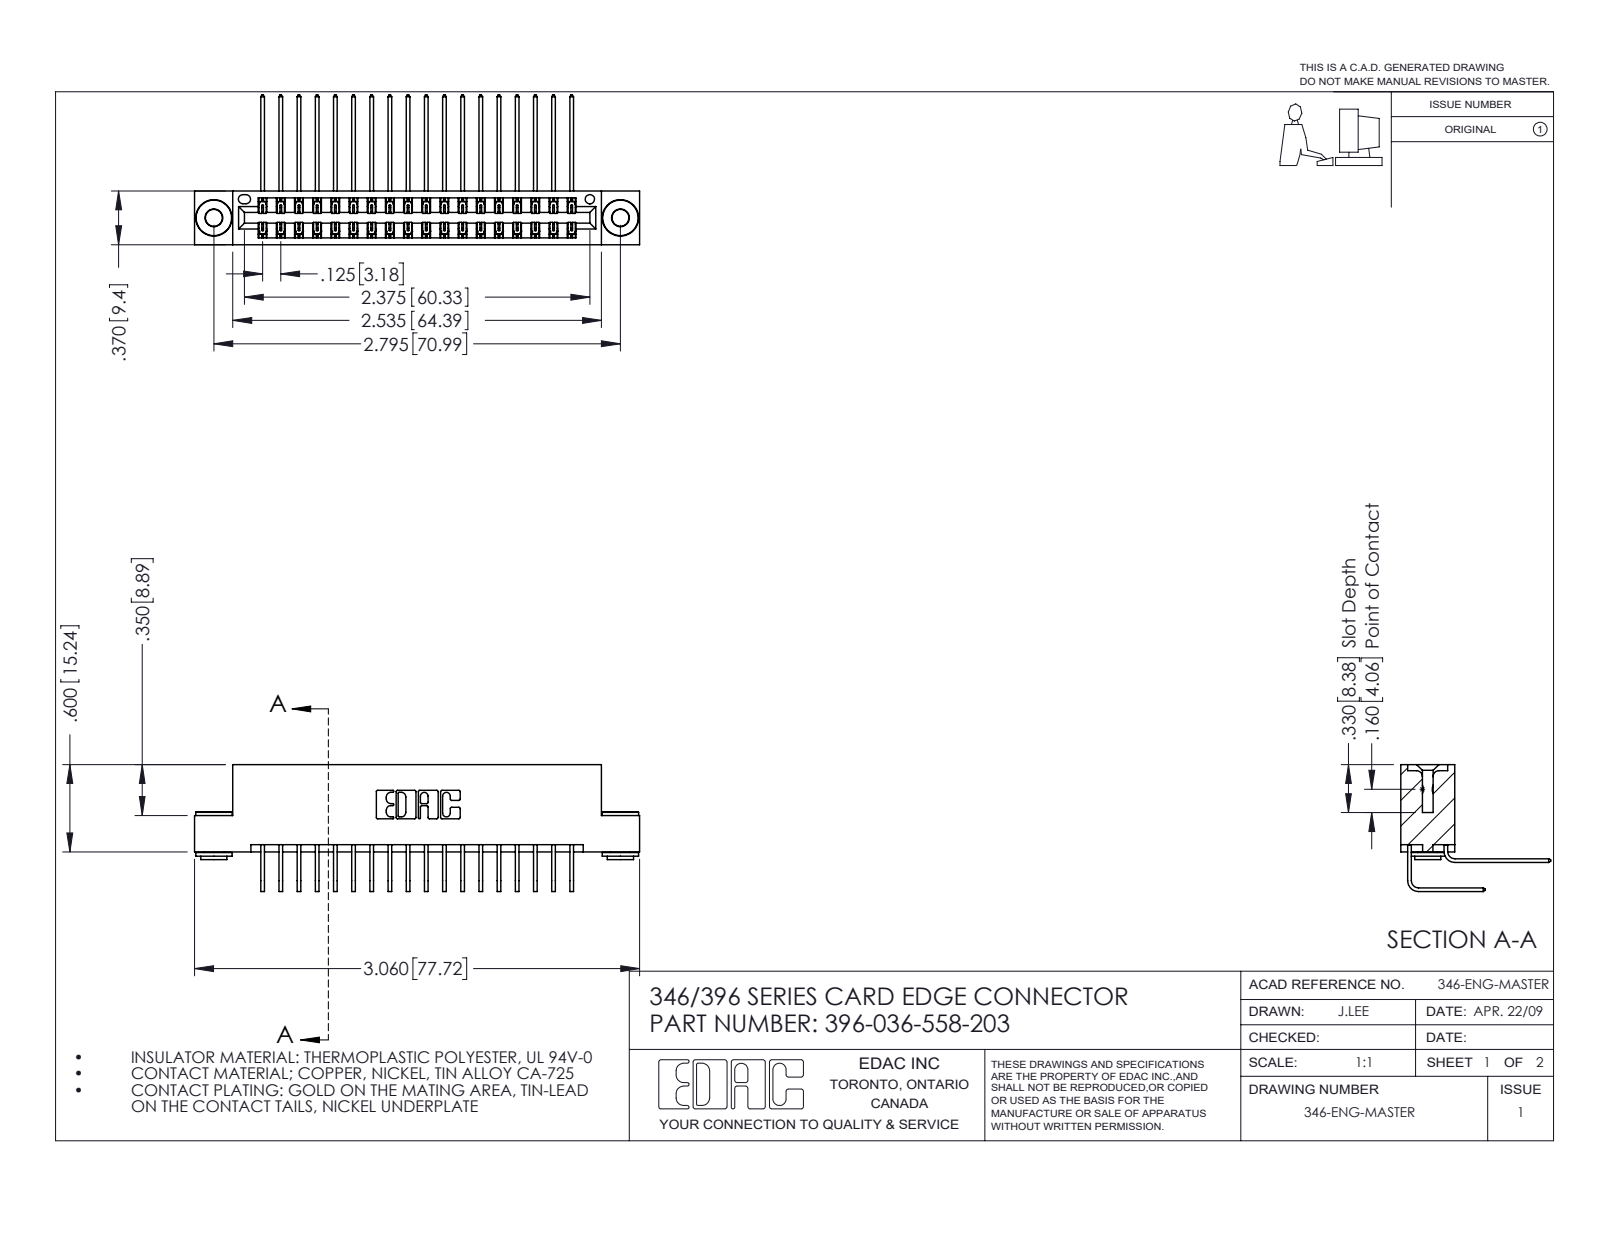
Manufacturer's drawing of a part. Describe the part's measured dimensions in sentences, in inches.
The part is named "345-250-002_345-250-002-102; 396-036-558-203; 346 Part_Flush Mounting Lugs - 0.156 Dia-TH; 345-292-001_558 Tail - 2 (+1 more)". Its 3-D file was written by "SolidWorks 2016 (CONFIG_CONTROL_DESIGN)". It is 39 solids with 2104 faces: 1418 planar, 678 cylindrical and 8 other. Overall it measures 3.06 by 1.03 by 0.873 inches. Its volume is 0.465 cubic inches and its surface area 17.53 square inches. Round holes: 2 of diameter 0.116, 2 of diameter 0.156, 1 of diameter 0.064. Round bosses or shafts: 2 of diameter 0.25, 2 of diameter 0.18, 2 of diameter 0.136. Partial cylindrical surfaces (rounded edges, fillets, slot ends): 54 of radius 0.006, 22 of radius 0.01, 6 of radius 0.007, 6 of radius 0.031, 3 of radius 0.026, 2 of radius 0.014, 2 of radius 0.022, 2 of radius 0.024. The main face-to-face distances are 0.322, 0.048, 0.25, 0.025, 0.37, 0.298, 0.072, 0.275, 0.148, 0.222. The hole center spacings are 0.246, 2.588, 2.795.
